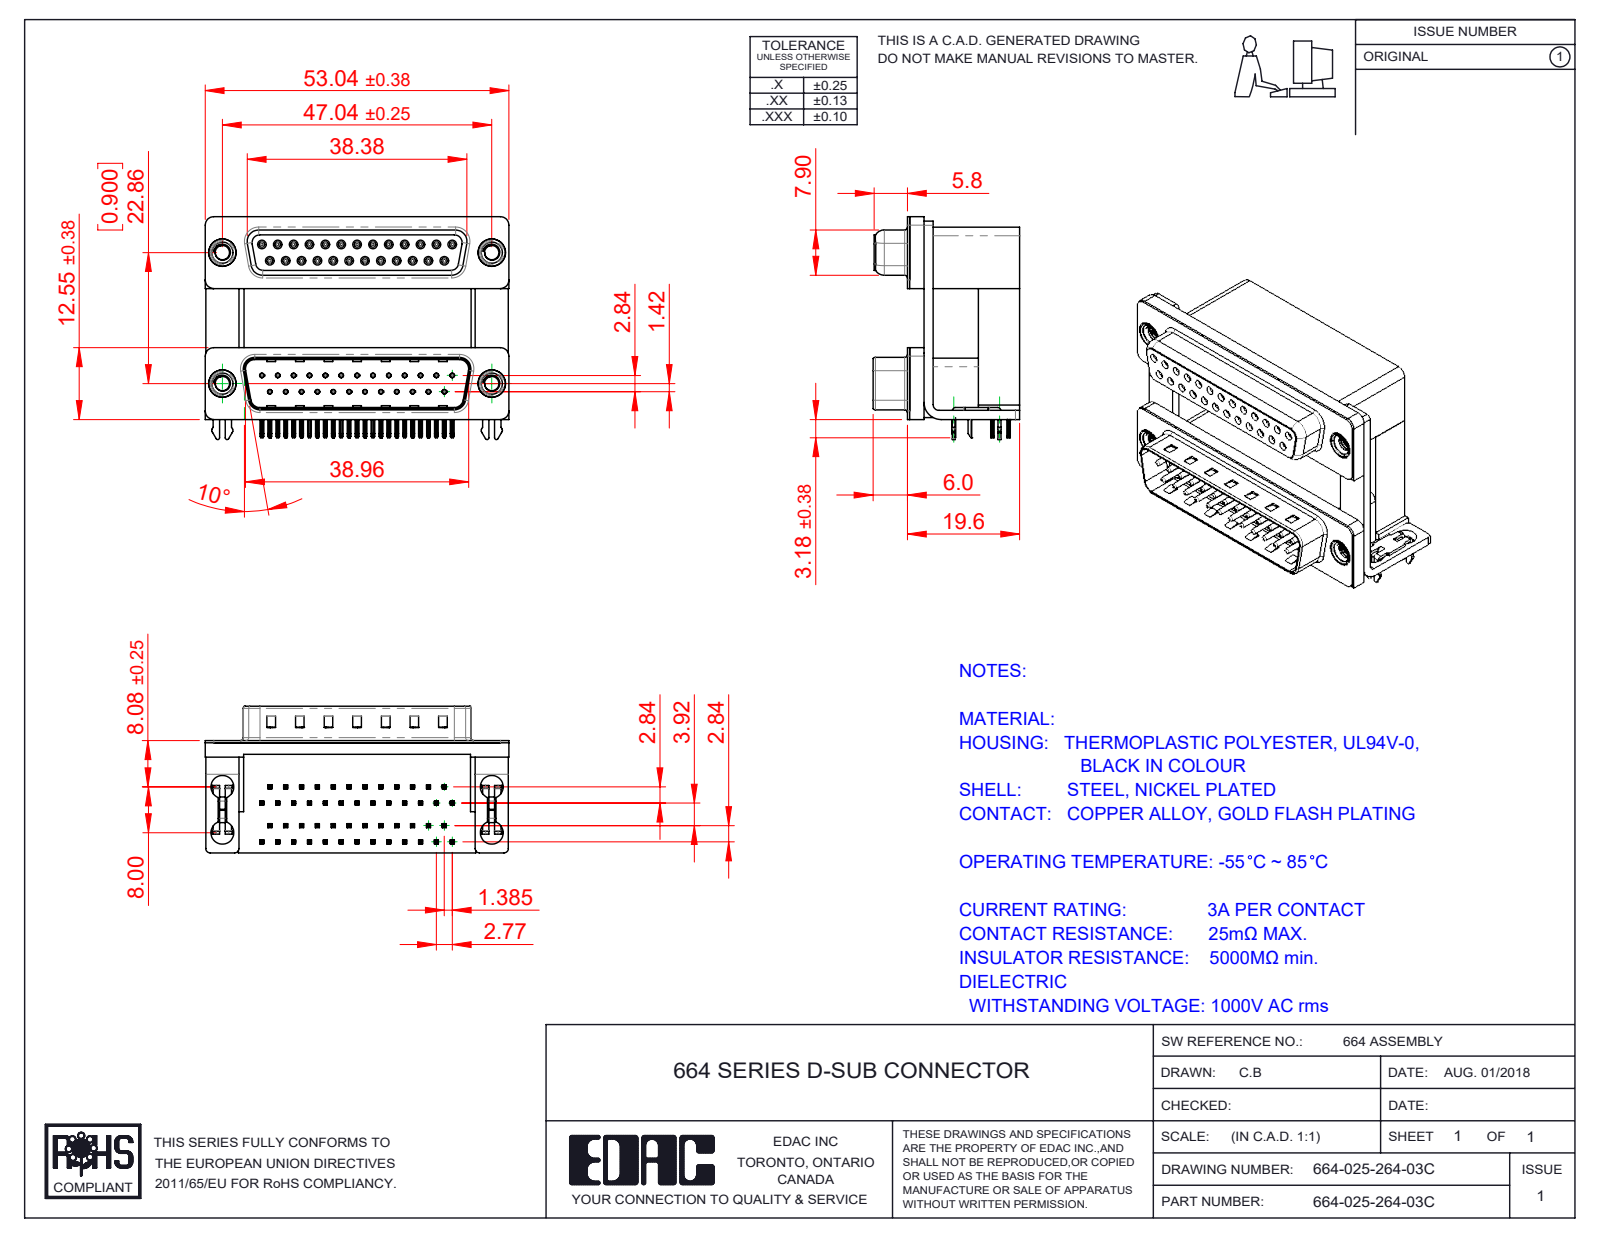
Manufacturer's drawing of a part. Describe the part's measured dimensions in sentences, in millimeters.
The part is named "664 Contact Top Upper_H; 664 2 Prong Board Lock_3; 664-025-264-03C; 664 Shell Receptacle_25 Contacts (+8 more)". Its 3-D file was written by "SolidWorks 2020 (CONFIG_CONTROL_DESIGN)". It is 63 solids with 6359 faces: 3359 planar, 1601 cylindrical and 1399 other. Overall it measures 53.04 by 38.91 by 25.6 millimeters. Its volume is 23 625 cubic millimeters and its surface area 25 359 square millimeters. Round holes: 50 of diameter 0.8, 25 of diameter 0.35, 25 of diameter 0.9, 8 of diameter 4, 4 of diameter 2.5, 4 of diameter 3.5, 4 of diameter 4.8, 4 of diameter 5. Round bosses or shafts: 25 of diameter 1.2, 25 of diameter 0.75, 4 of diameter 4.9, 4 of diameter 4.75, 4 of diameter 3.9. Partial cylindrical surfaces (rounded edges, fillets, slot ends): 202 of radius 0.1, 110 of radius 0.25, 100 of radius 0.15, 50 of radius 0.12, 50 of radius 0.35, 25 of radius 0.34, 16 of radius 0.5, 14 of radius 1.5. The main face-to-face distances are 19.2, 12, 0.4, 7.2, 10.7, 2.84, 16.7, 9.5, 2.5, 12.4. The hole center spacings are 2.77, 3.16, 5.54, 8.31, 11.08, 13.85, 16.62, 5.03.
